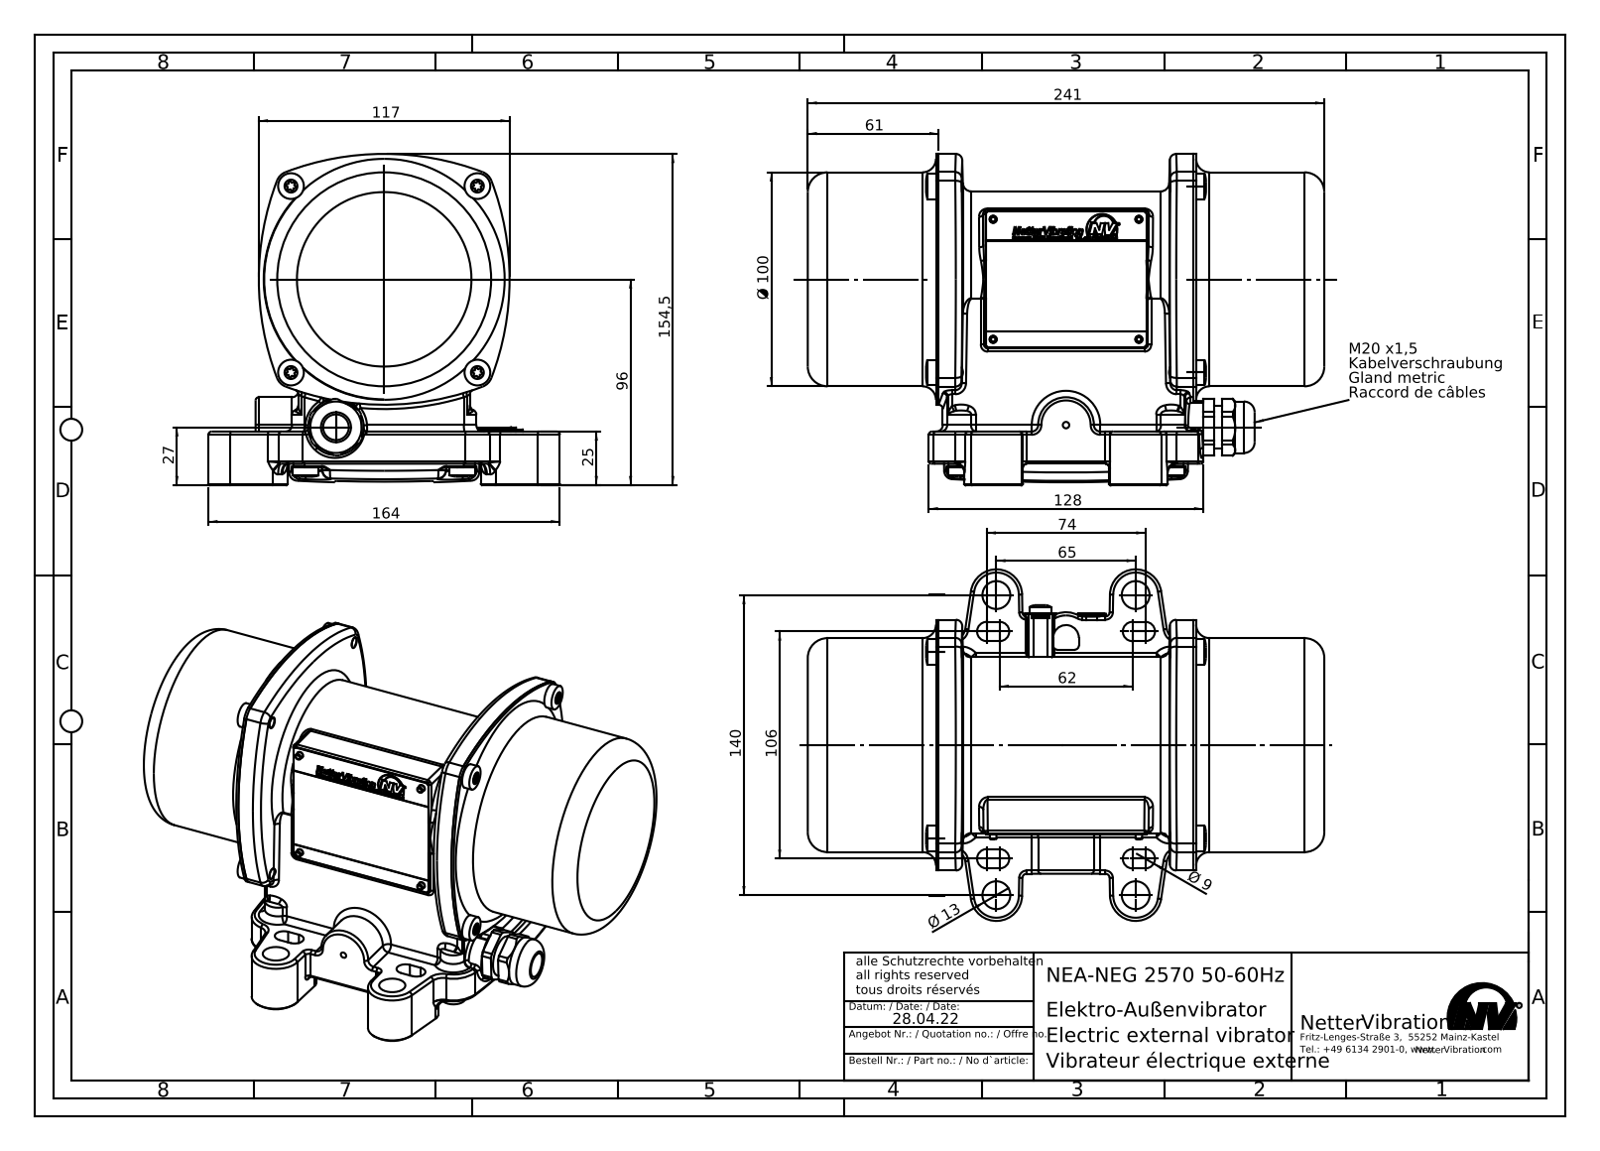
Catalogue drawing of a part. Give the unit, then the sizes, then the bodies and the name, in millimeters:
Units: millimetres
Overall size (bounding box): 241 × 164 × 154.5
Round holes (diameter × count): ⌀3.4 ×4, ⌀7 ×4, ⌀10.5 ×1, ⌀11.5 ×1, ⌀12 ×1, ⌀13 ×1, ⌀14.5 ×1, ⌀18.5 ×1, ⌀84 ×1, ⌀97.4 ×1
Round bosses / shafts (diameter × count): ⌀12 ×8, ⌀6 ×8, ⌀99.8 ×1, ⌀24 ×1, ⌀20 ×1, ⌀13 ×1, ⌀10 ×1, ⌀5 ×1
Partial cylindrical surfaces — rounded edges, fillets, slot ends (radius × count): R1.5 ×59, R0.5 ×49, R0.2 ×41, R2 ×28, R1 ×26, R3 ×16, R6 ×15, R1.75 ×9
Main face-to-face distances: 1.2, 59.8, 180, 239.8, 61, 178.8, 2, 0.5, 81, 9
Hole centre spacings: 61.5, 86.98, 56, 68, 88.09, 123.01, 24.25, 33.04
Volume: 699 332 mm³ · Surface area: 349 431 mm²
Bodies: 21 solids, 2971 faces (759 planar, 746 cylindrical, 1466 other)
Part name (STEP PRODUCT): NEA-NEG 2570-50-60Hz
STEP written by: SolidWorks 2015 (AUTOMOTIVE_DESIGN)
